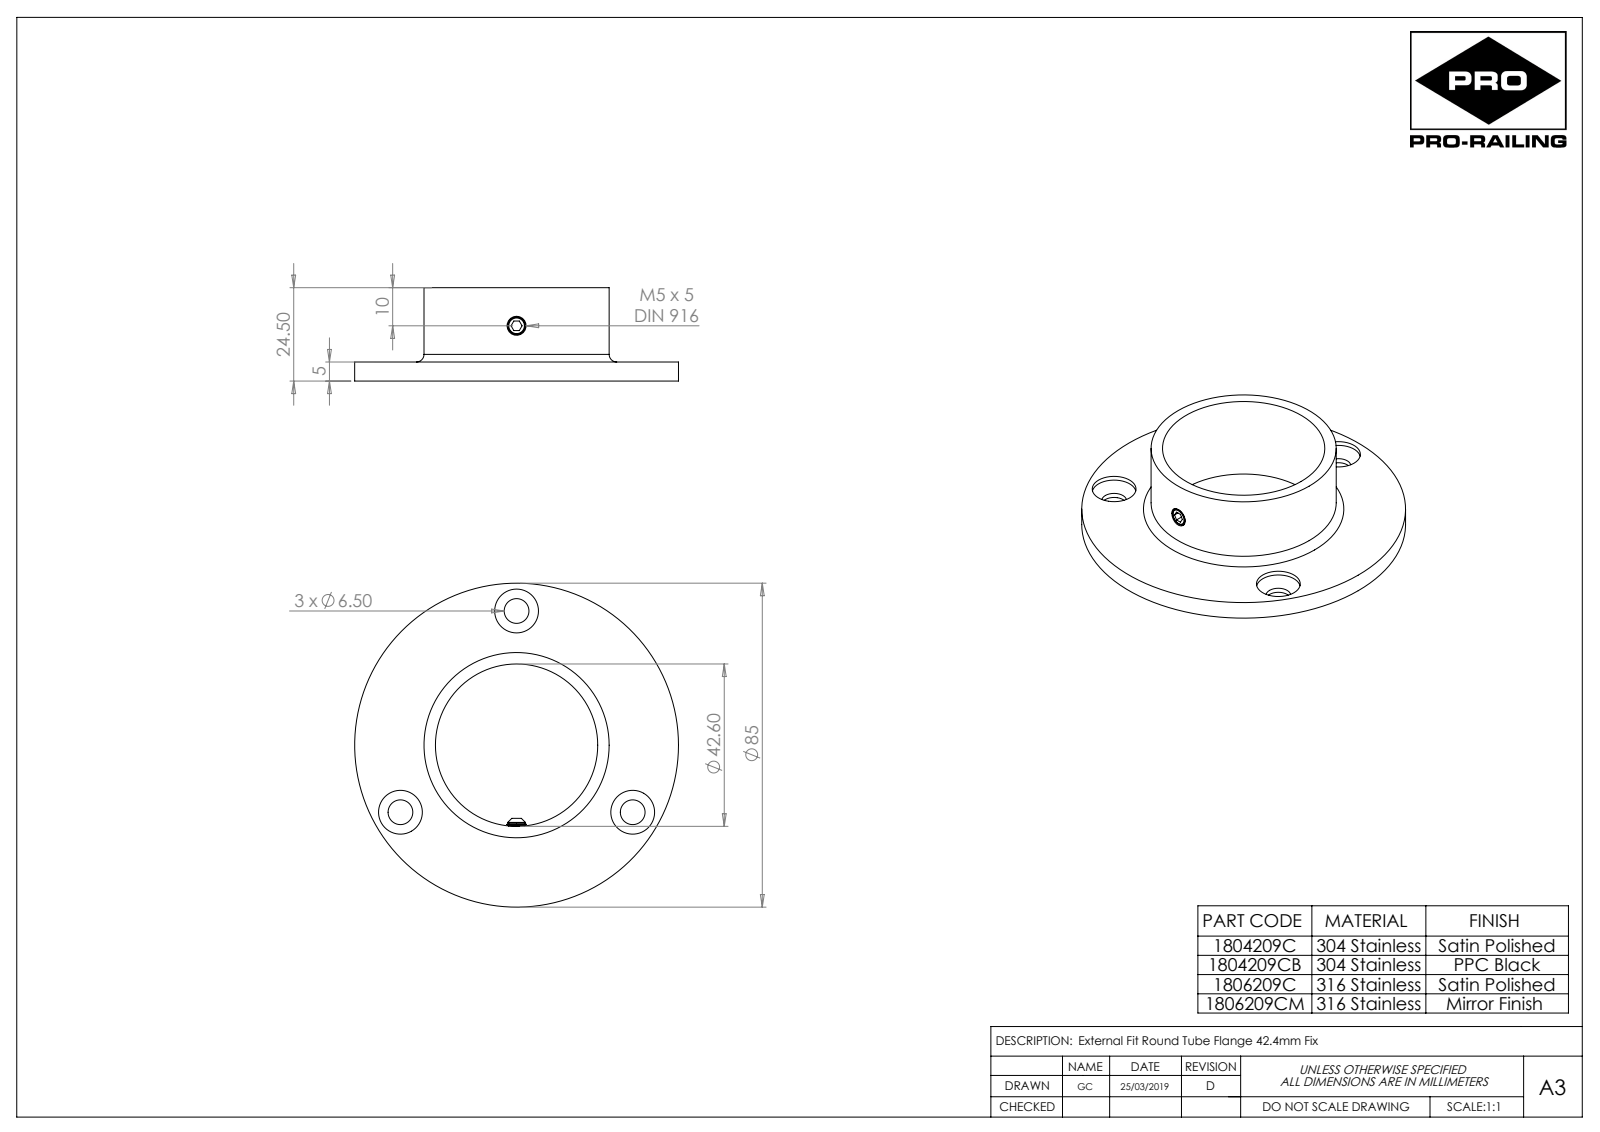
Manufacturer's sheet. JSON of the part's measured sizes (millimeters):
{"part_name": "1806209C", "step_written_by": "SolidWorks 2018 (AUTOMOTIVE_DESIGN)", "units": "millimeters", "bodies": {"solids": 1, "faces": 31, "planar": 3, "cylindrical": 20, "other": 8}, "overall_size": [85, 85, 24.5], "volume_mm3": 28708, "surface_area_mm2": 16067, "round_holes": [[6.5, 3], [11.5, 3], [5, 1], [42.6, 1]], "round_bosses_or_shafts": [[85, 1], [48.6, 1]], "face_to_face_distances": [5, 24.5, 19.5], "hole_center_spacings": [35.2, 60.97, 60.96]}
